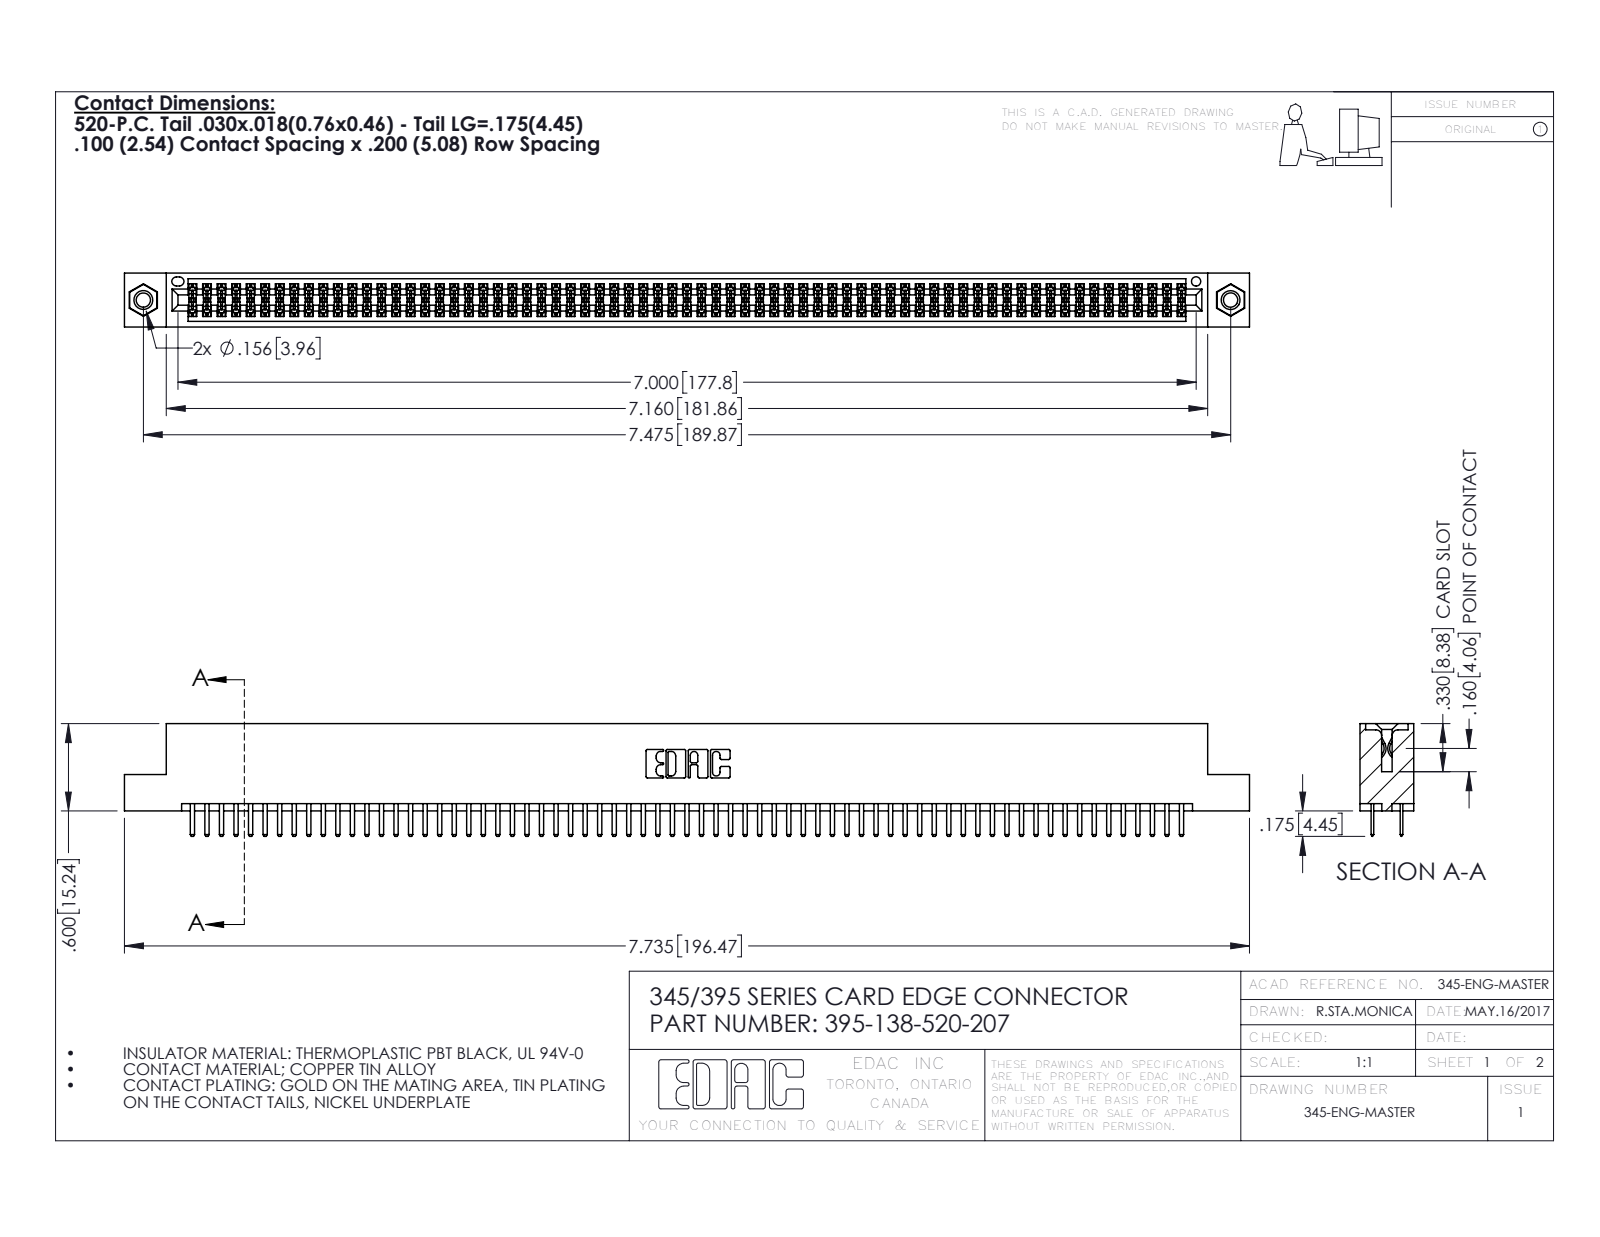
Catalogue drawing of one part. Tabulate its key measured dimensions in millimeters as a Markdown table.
| quantity | value |
| --- | --- |
| part name | 345-250-001_345-250-005-103; 345 Part_Flush Mounting Lugs - 0.156 Dia-TI; 395-138-520-207; 345-292-001_345-293-120 |
| STEP written by | SolidWorks 2016 (CONFIG_CONTROL_DESIGN) |
| units | millimeters |
| bodies | 141 solids, 7638 faces (4942 planar, 2680 cylindrical, 16 other) |
| overall size | 196.5 × 19.7 × 9.4 |
| volume | 19 250 mm³ |
| surface area | 28 900 mm² |
| round holes (diameter × count) | 2.5 × 2, 3.2 × 2, 4 × 2, 1.6 × 1 |
| round bosses / shafts (diameter × count) | 3.9 × 2 |
| partial cylindrical surfaces (radius × count) | 0.2 × 207, 0.3 × 142, 0.3 × 22, 0.2 × 6, 0.8 × 6, 0.7 × 3, 0.4 × 2, 0.5 × 2 |
| main face-to-face distances | 1.8, 7.6, 5.1, 9.4, 2.5, 6.9, 0.6, 5.7, 0.6, 1.8 |
| hole center spacings | 6.9, 183.9, 189.9 |
